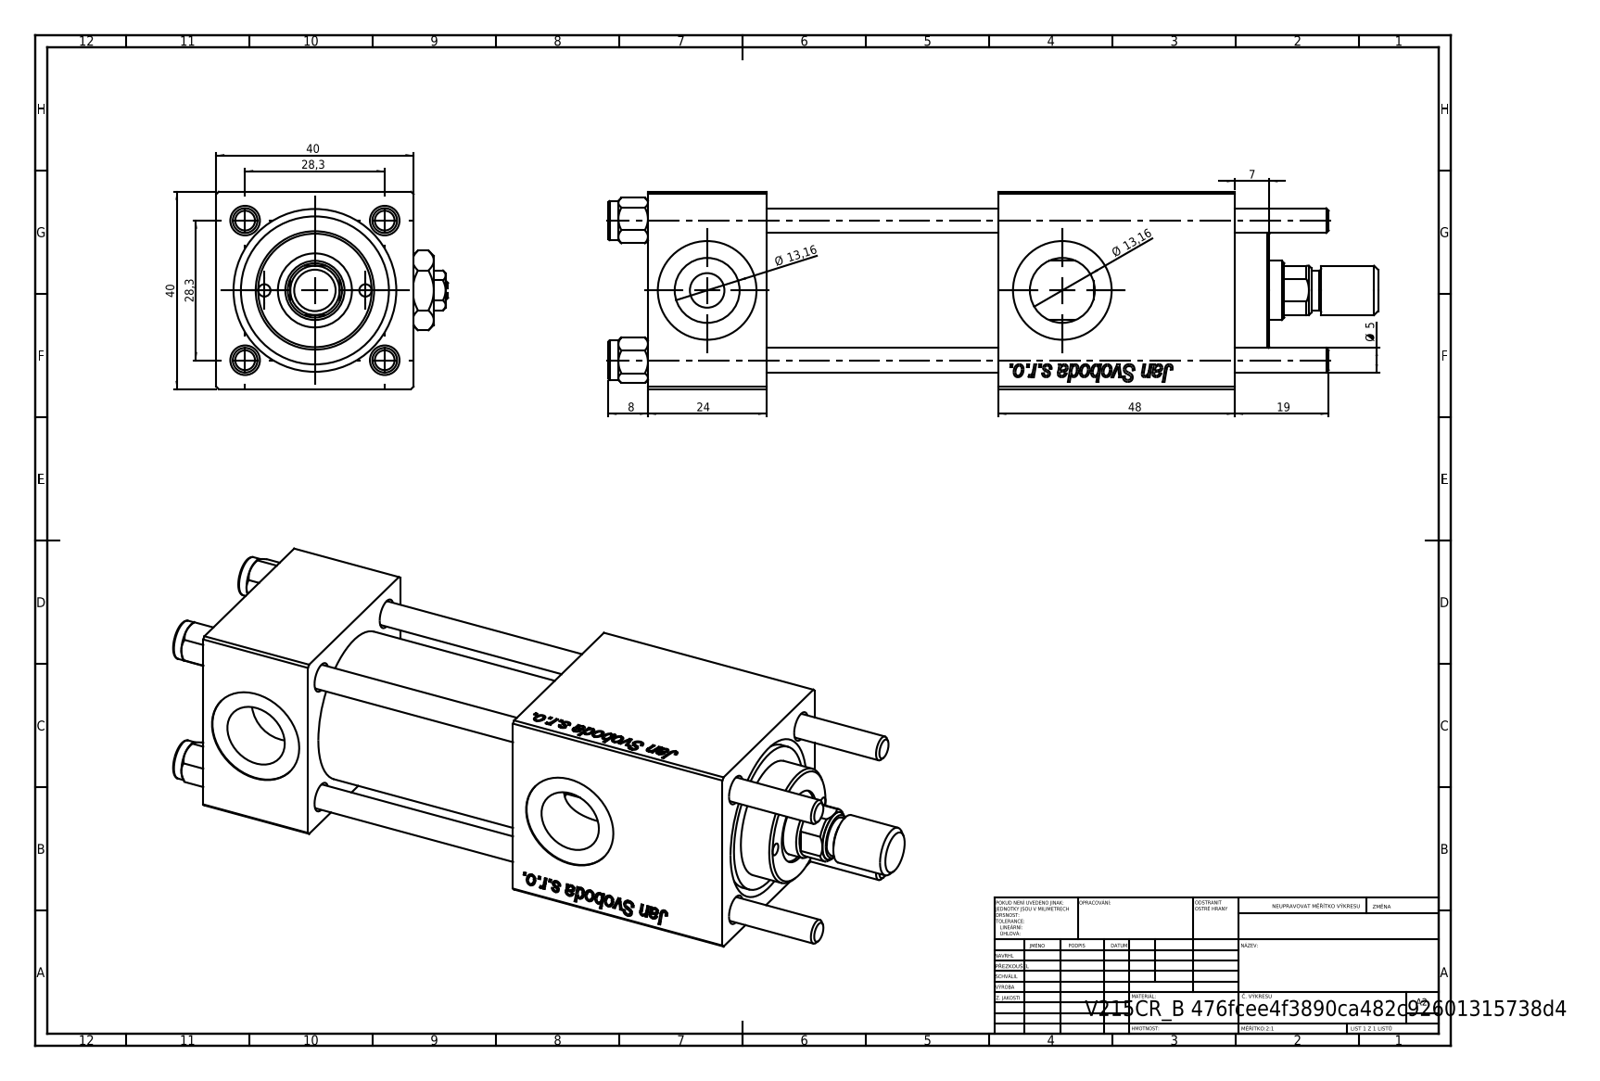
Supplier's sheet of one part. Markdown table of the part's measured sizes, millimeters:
| quantity | value |
| --- | --- |
| part name | V215_VC_A; ROD_END_AH; Zatka_pro_OIL_PORT; V215CR_B-1 (+3 more) |
| STEP written by | SolidWorks 2019 (CONFIG_CONTROL_DESIGN) |
| units | millimeters |
| bodies | 13 solids, 1228 faces (458 planar, 94 cylindrical, 676 other) |
| overall size | 156 × 47 × 40 |
| volume | 145 044 mm³ |
| surface area | 60 442 mm² |
| round holes (diameter × count) | 5 × 4, 20 × 3, 2.5 × 2, 7 × 2, 13.16 × 2, 6.5 × 1, 12 × 1, 15 × 1, 25 × 1, 30 × 1 |
| round bosses / shafts (diameter × count) | 8 × 5, 31 × 1, 24 × 1, 10 × 1 |
| partial cylindrical surfaces (radius × count) | 5.5 × 1 |
| main face-to-face distances | 40, 24, 90.3, 66.3, 119, 47, 71, 19.3, 95, 48 |
| hole center spacings | 14.68, 20.01, 28.21, 28.3, 10.25, 40.02, 20.5, 72 |
